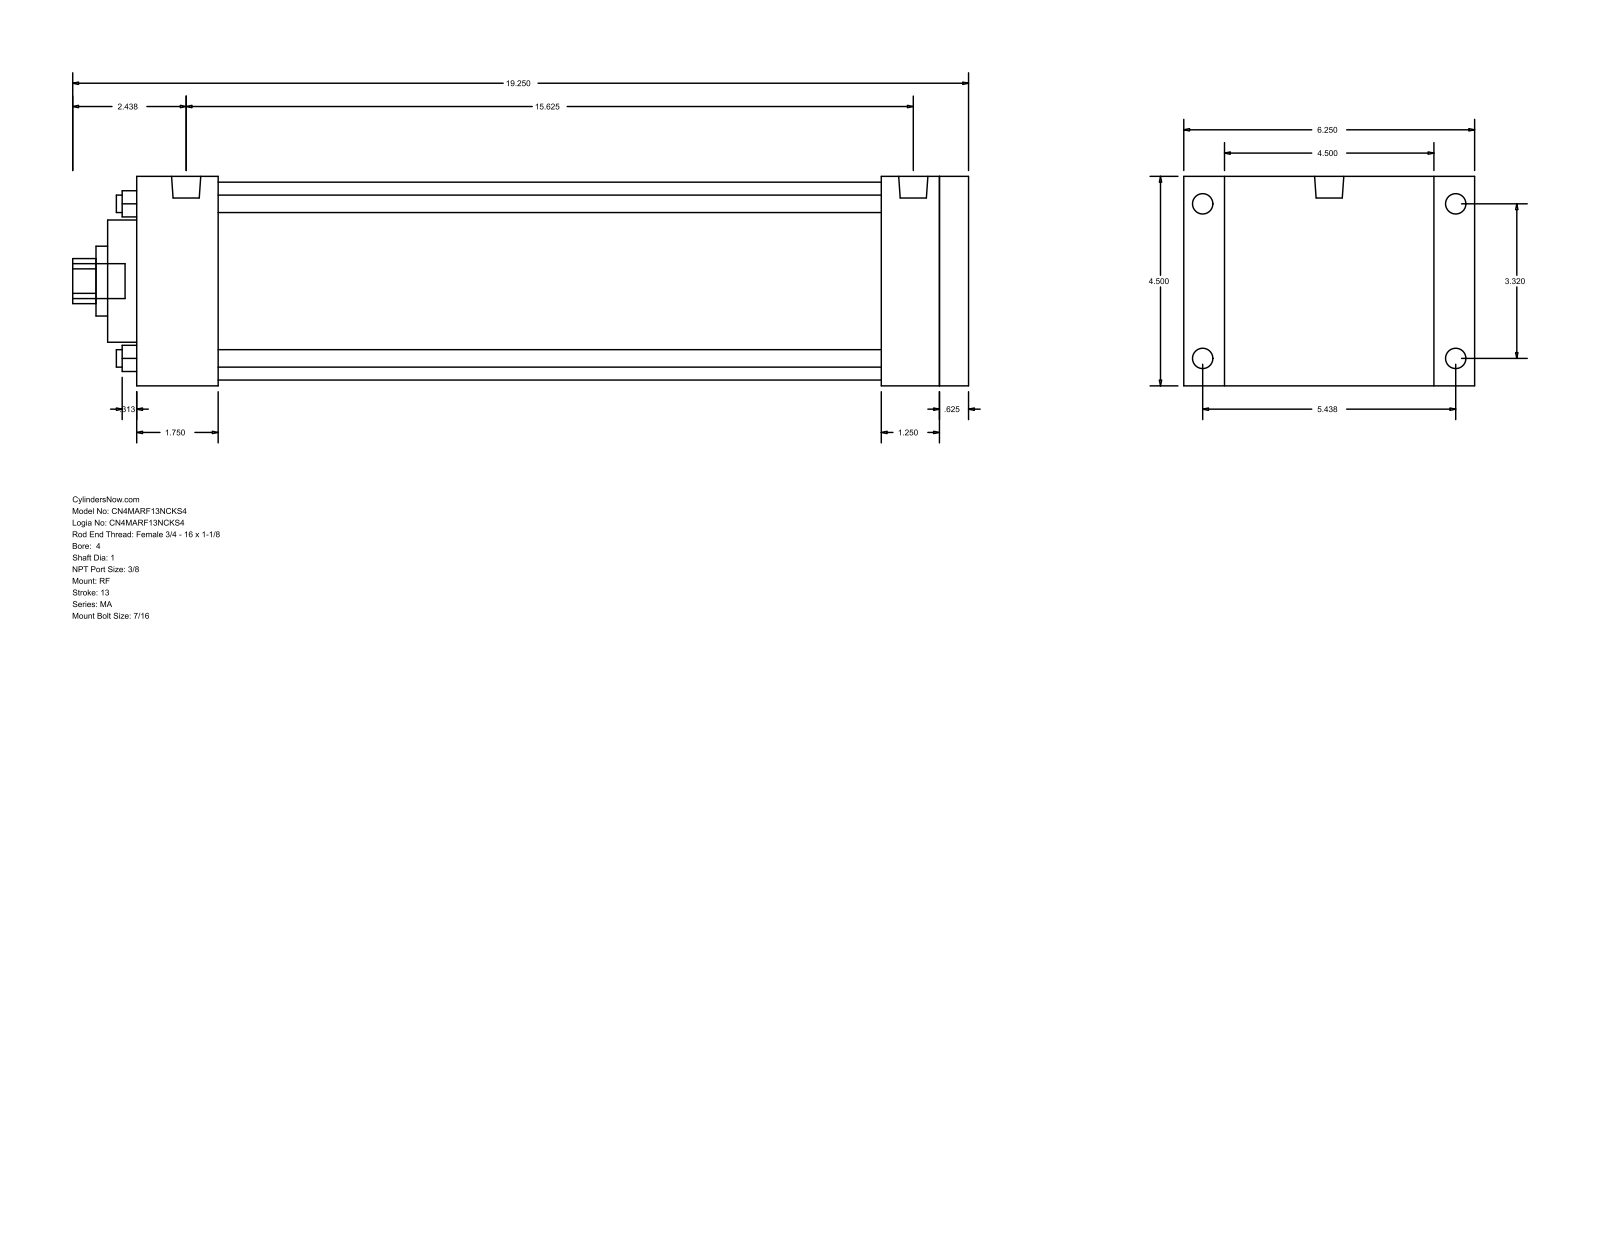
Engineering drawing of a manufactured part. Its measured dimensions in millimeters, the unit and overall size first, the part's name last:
Units: millimetres
Overall size (bounding box): 488.95 × 158.75 × 114.3
Round holes (diameter × count): ⌀9.53 ×4, ⌀25.4 ×1, ⌀38.1 ×1, ⌀66.67 ×1, ⌀107.95 ×1
Round bosses / shafts (diameter × count): ⌀11.11 ×8, ⌀15.93 ×2, ⌀19.05 ×1
Partial cylindrical surfaces — rounded edges, fillets, slot ends (radius × count): R12.29 ×1
Main face-to-face distances: 114.3, 454.03, 438.15, 15.88, 22.23, 136.53, 406.4, 31.75, 47.63, 44.46
Hole centre spacings: 59.62, 84.32, 119.25
Bodies: 0 solids, 94 faces (65 planar, 29 cylindrical, 0 other)
Part name (STEP PRODUCT): MA_RF__0400_1
STEP written by: GSSL Pune (CONFIG_CONTROL_DESIGN)
